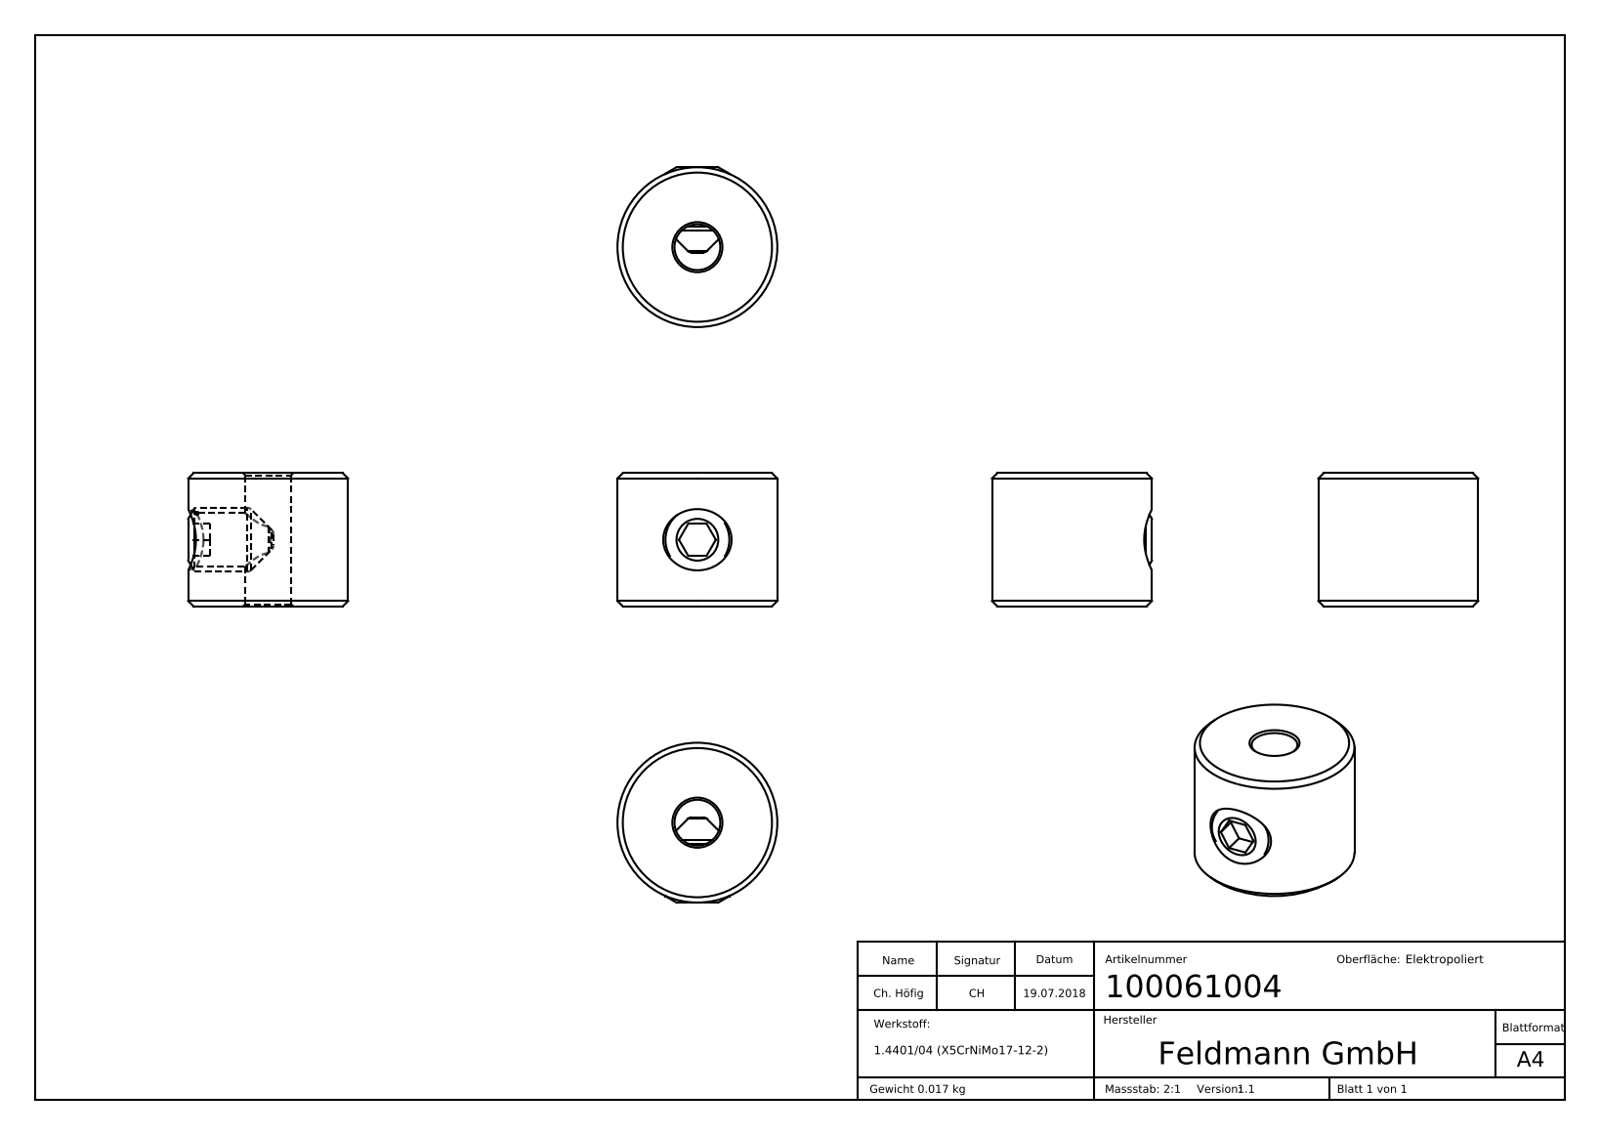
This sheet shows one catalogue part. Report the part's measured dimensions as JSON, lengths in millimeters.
{"part_name": "10006100X Teil1_100061004 Teil1; DIN914_DIN 914 M6x8; 100061004", "step_written_by": "SolidWorks 2015 (CONFIG_CONTROL_DESIGN)", "units": "millimeters", "bodies": {"solids": 2, "faces": 251, "planar": 120, "cylindrical": 8, "other": 123}, "overall_size": [15, 15, 12.5], "volume_mm3": 2068, "surface_area_mm2": 1286, "round_holes": [[4.3, 1], [5, 1]], "round_bosses_or_shafts": [[15, 1], [6, 1]], "face_to_face_distances": [12.5, 3, 4.75, 7.75, 2, 6, 8, 12.4, 7.65, 4.65]}
